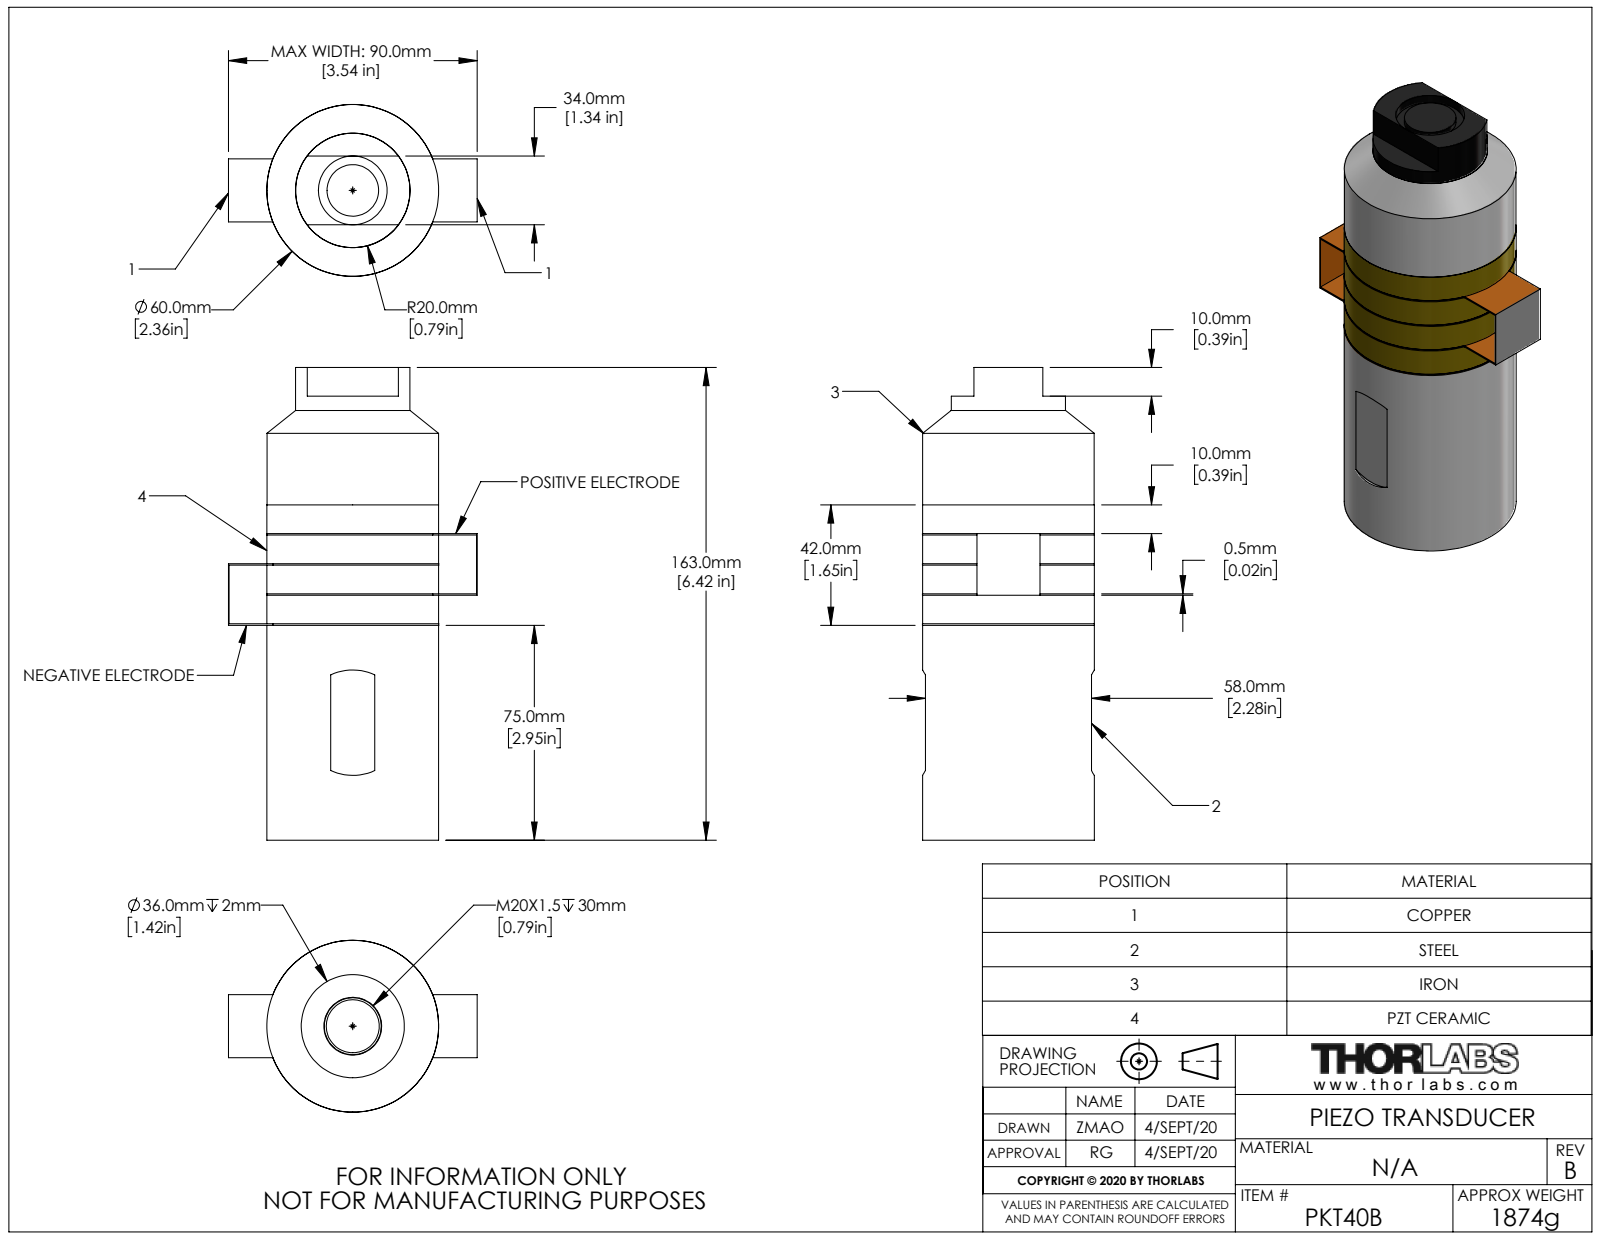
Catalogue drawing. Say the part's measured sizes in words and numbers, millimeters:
The part is named "CTN016252-E0W". Its 3-D file was written by "SolidWorks 2018 (AUTOMOTIVE_DESIGN)". It is 1 solid with 90 faces: 46 planar, 40 cylindrical and 4 other. Overall it measures 165 by 86.83 by 60.01 millimeters. Its volume is 412 740 cubic millimeters and its surface area 44 013 square millimeters. Round holes: 1 of diameter 18.5, 1 of diameter 24, 1 of diameter 30, 1 of diameter 36. Round bosses or shafts: 1 of diameter 60.01, 1 of diameter 60, 1 of diameter 59.9, 1 of diameter 39.9, 1 of diameter 18. Partial cylindrical surfaces (rounded edges, fillets, slot ends): 1 of radius 18.39. The main face-to-face distances are 10, 10.5, 21, 0.5, 85.5, 75.5, 2, 11, 86.64, 58.
